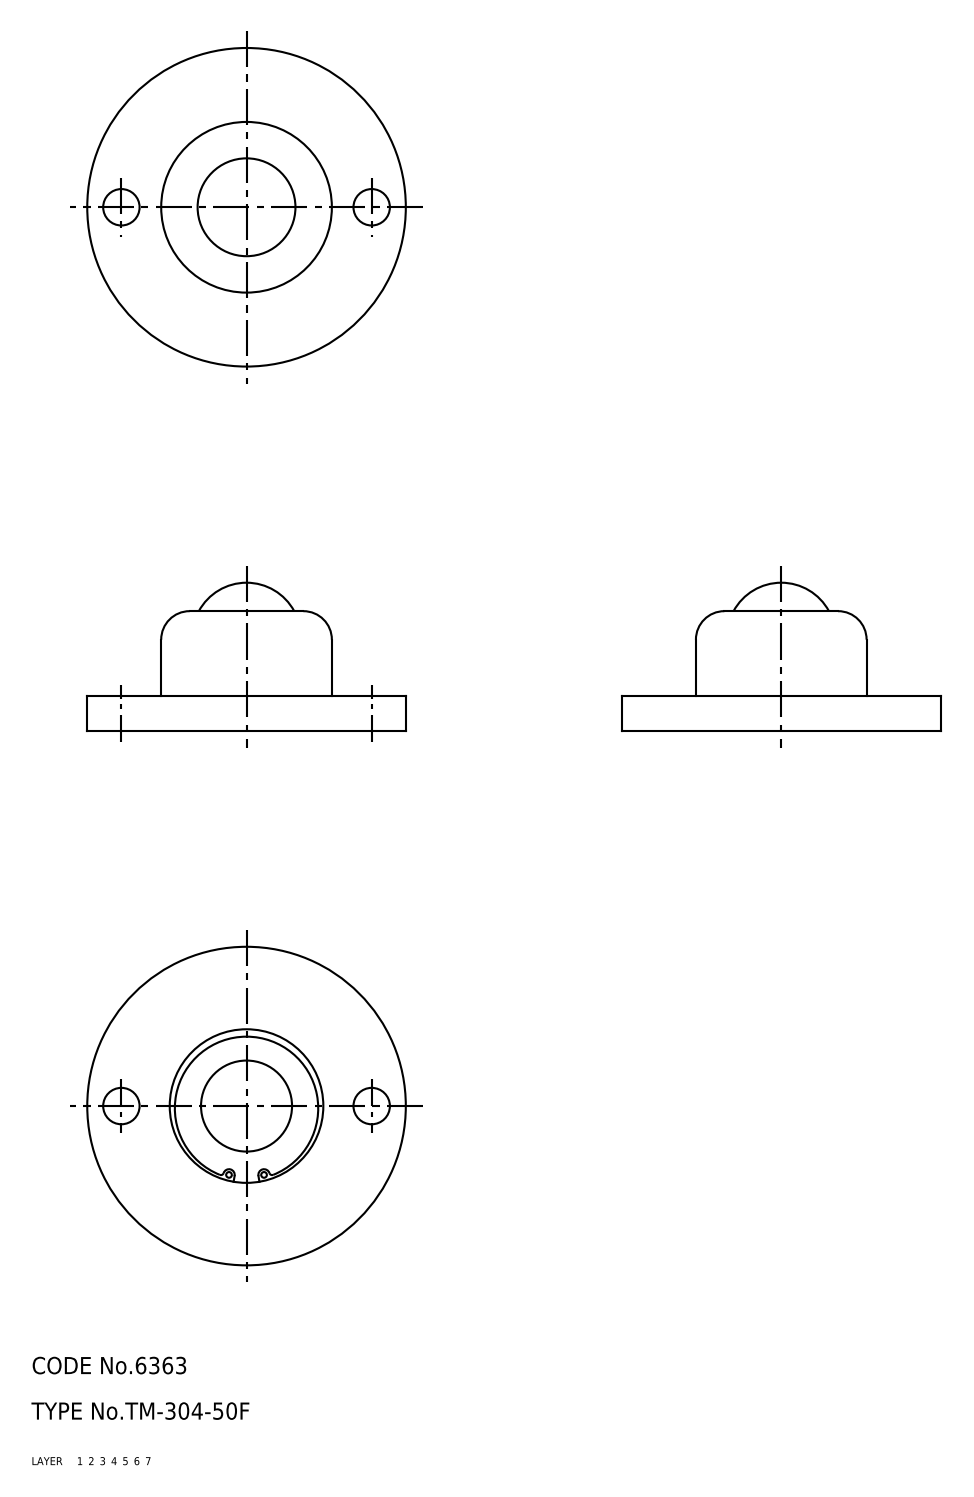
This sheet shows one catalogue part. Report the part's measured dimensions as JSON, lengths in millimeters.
{"part_name": "67112346; 67112359", "step_written_by": "CADfix (AUTOMOTIVE_DESIGN)", "units": "millimeters", "bodies": {"solids": 2, "faces": 43, "planar": 0, "cylindrical": 0, "other": 43}, "overall_size": [56, 56, 26], "volume_mm3": 18154, "surface_area_mm2": 10809}
